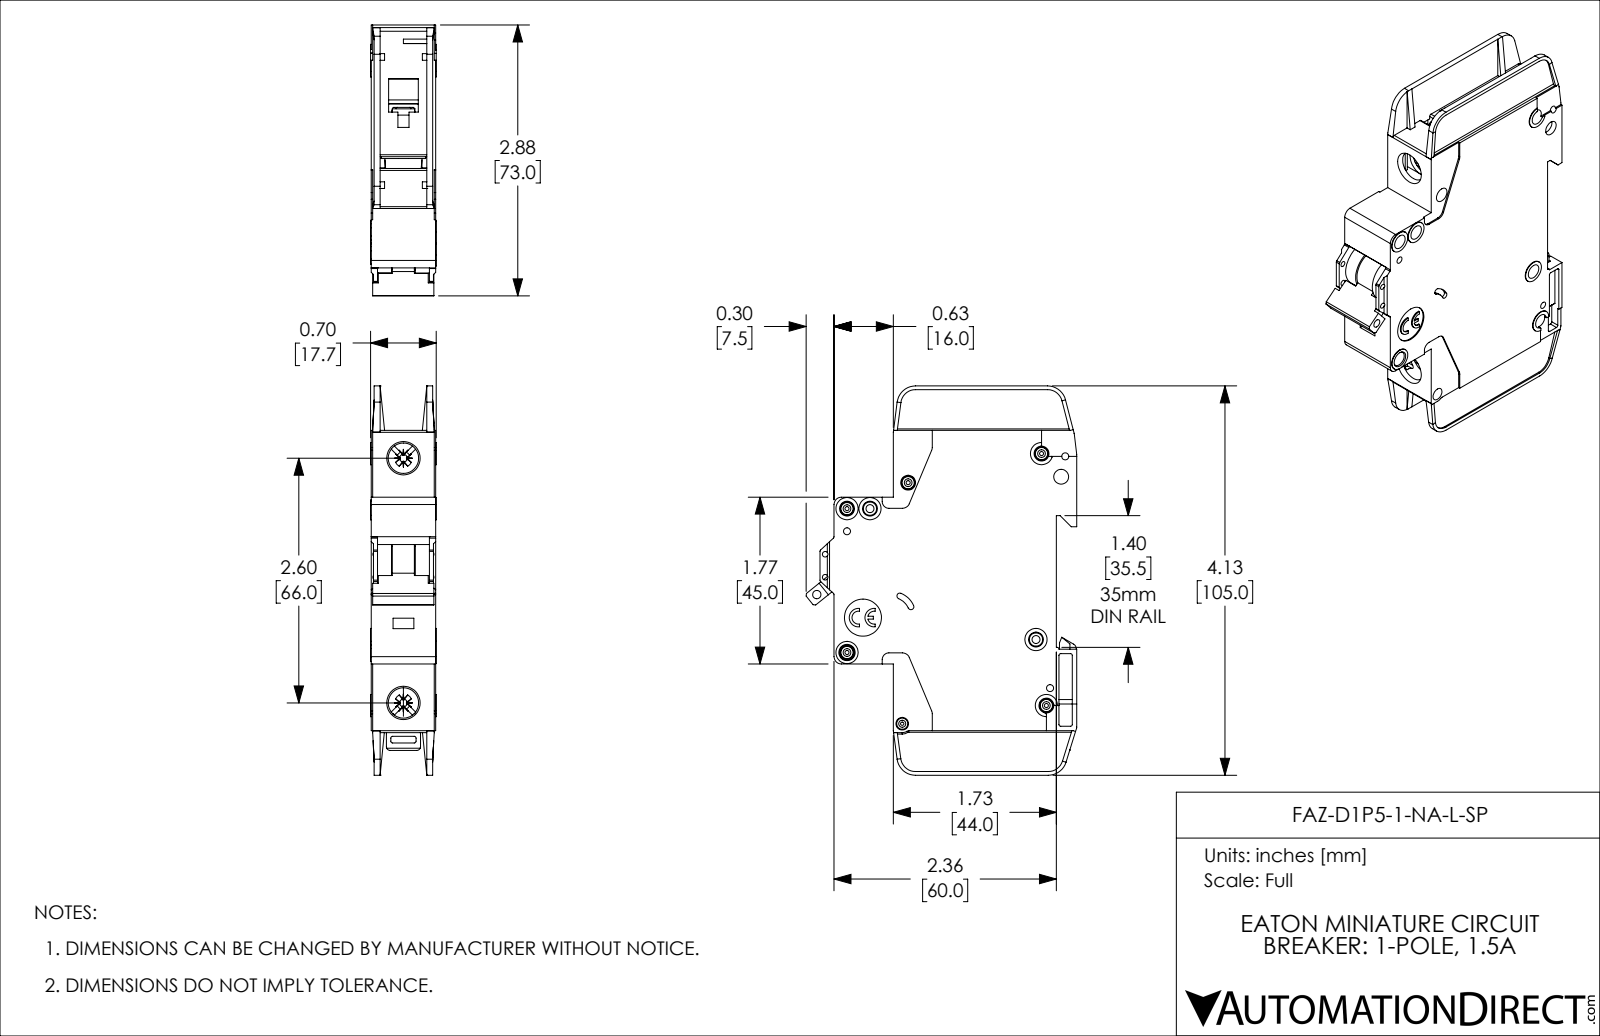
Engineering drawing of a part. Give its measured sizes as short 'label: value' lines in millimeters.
name: FAZ-D1P5-1-NA-L-SP
written by: SolidWorks 2019 (AUTOMOTIVE_DESIGN)
unit: mm
bodies: 1 solid, 1127 faces (671 planar, 357 cylindrical, 99 other)
size: 105 × 73.1 × 17.7
volume: 76 720 mm³; area: 26 460 mm²
holes: 8× ⌀4, 5× ⌀1.1, 4× ⌀1.9, 2× ⌀1.5, 2× ⌀2.2, 2× ⌀8.2, 1× ⌀0.9, 1× ⌀2.3, 1× ⌀2.5, 1× ⌀3.4, 1× ⌀10
bosses: 5× ⌀3.3, 4× ⌀6, 2× ⌀3, 1× ⌀2.5
rounds: 42× R0.5, 10× R0.4, 10× R1, 8× R2, 5× R5, 4× R0.2, 4× R0.7, 4× R1.1
face distances: 1.2, 17.4, 15, 16.2, 2.4, 13.8, 0.4, 0.8, 12.6, 14.6
hole spacings: 6.2, 13.6, 22.1, 4.8, 5.1, 5.2, 5.6, 6.1
